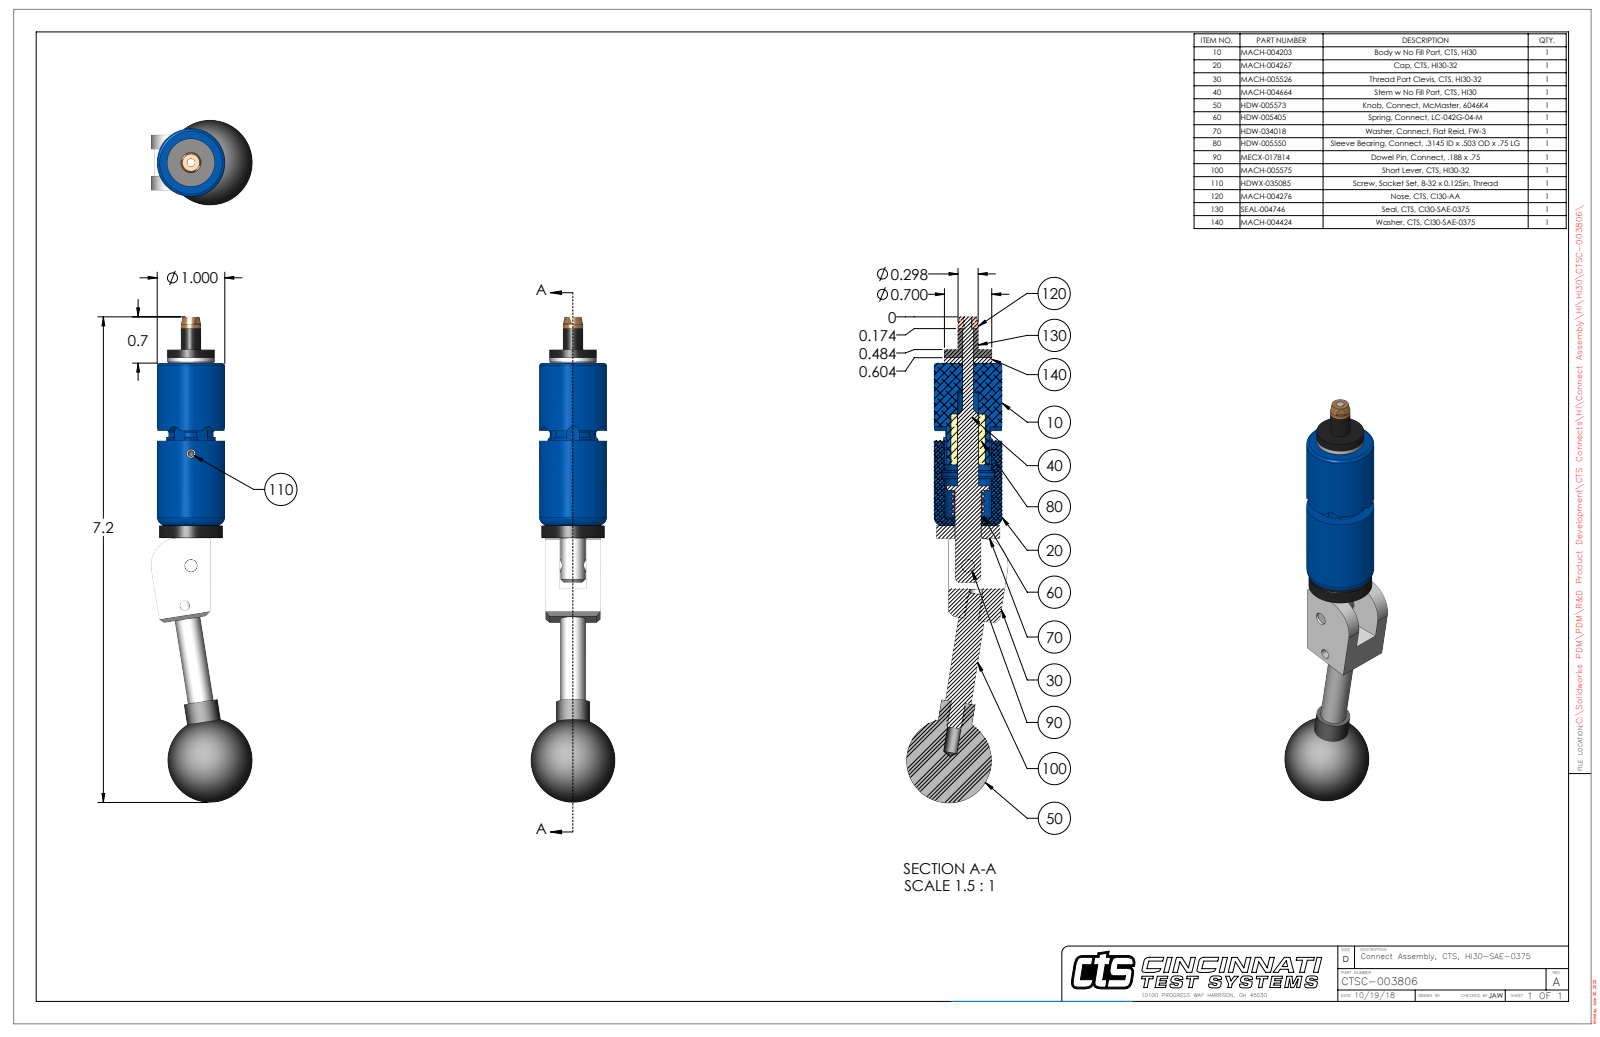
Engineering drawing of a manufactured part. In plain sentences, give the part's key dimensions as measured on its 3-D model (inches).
The part is named "CTSC-003806". Its 3-D file was written by "SolidWorks 2023 (AUTOMOTIVE_DESIGN)". It is 9 solids with 265 faces: 99 planar, 108 cylindrical and 58 other. Overall it measures 7.181 by 1.492 by 1.25 inches. Its volume is 3.851 cubic inches and its surface area 31.05 square inches. Round holes: 2 of diameter 0.201, 1 of diameter 0.113, 1 of diameter 0.136, 1 of diameter 0.15, 1 of diameter 0.155, 1 of diameter 0.161, 1 of diameter 0.164, 1 of diameter 0.189, 1 of diameter 0.385, 1 of diameter 0.392, 1 of diameter 0.688. Round bosses or shafts: 1 of diameter 1, 1 of diameter 0.936, 1 of diameter 0.7, 1 of diameter 0.5, 1 of diameter 0.38, 1 of diameter 0.375, 1 of diameter 0.3, 1 of diameter 0.297. Partial cylindrical surfaces (rounded edges, fillets, slot ends): 6 of radius 0.093, 1 of radius 0.015, 1 of radius 0.375, 1 of radius 0.4, 1 of radius 0.476. The main face-to-face distances are 0.21, 0.602, 2.4, 0.812, 2.587, 0.187, 0.08, 2.48, 2.667, 0.391. The hole center spacings are 0.599, 1.658, 2.252.
